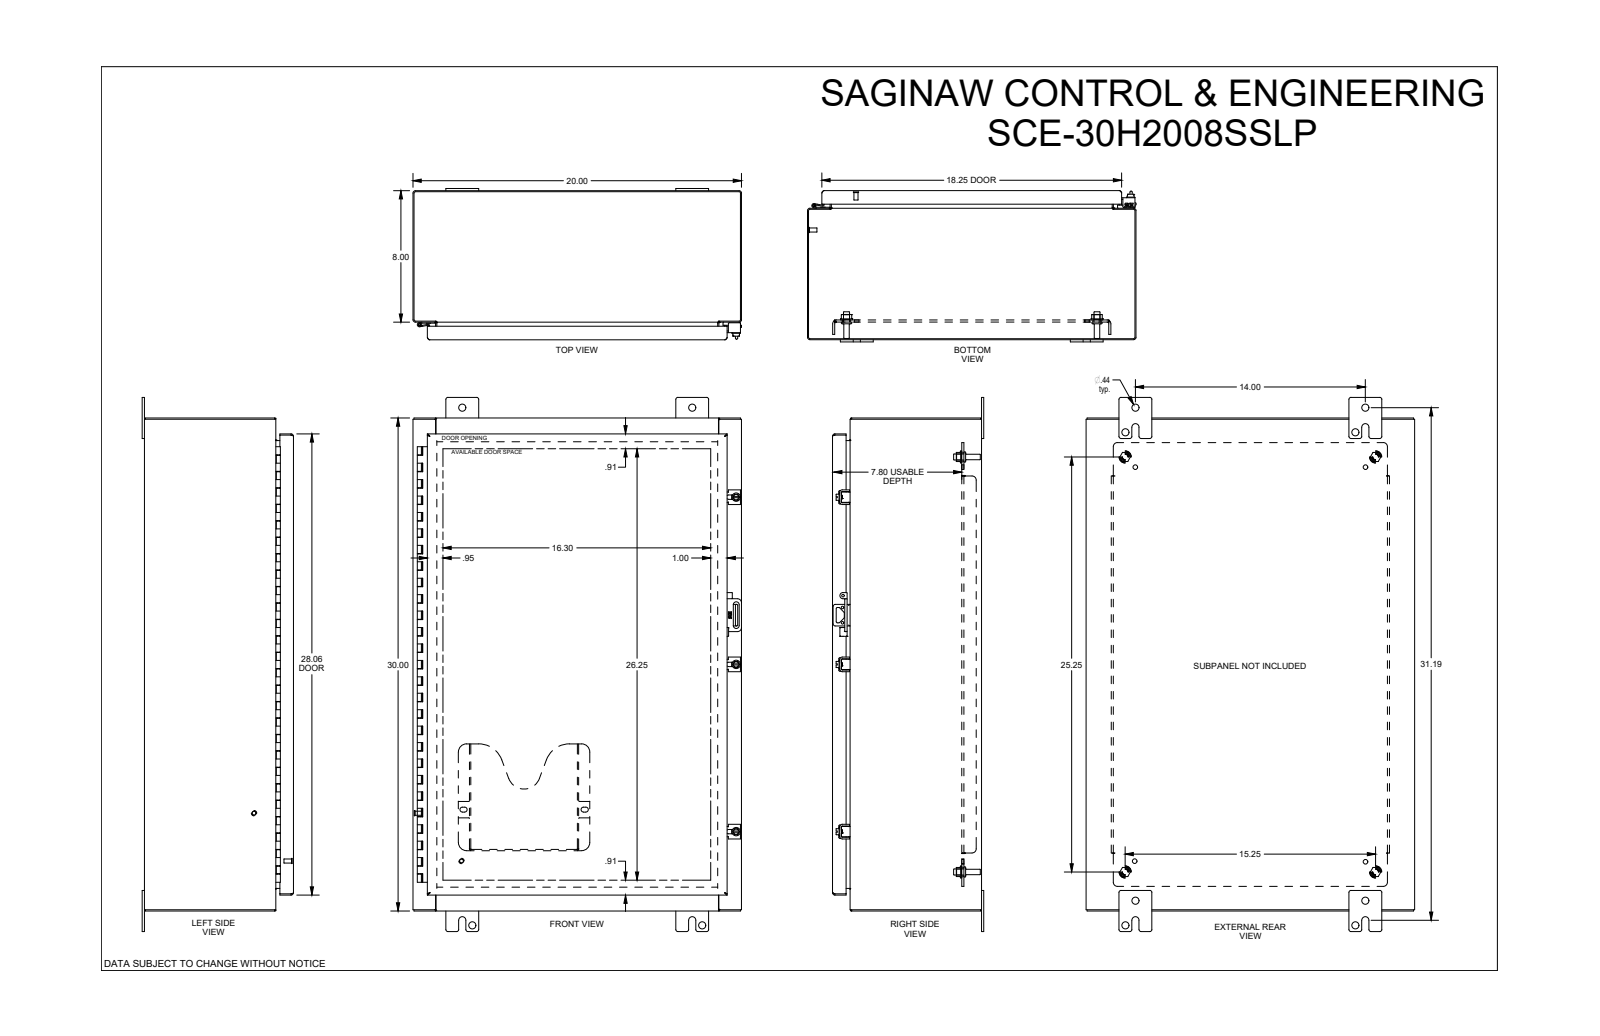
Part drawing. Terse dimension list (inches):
name: SCE-30H2008SSLP
written by: SolidWorks 2019 (CONFIG_CONTROL_DESIGN)
unit: in
bodies: 0 solids, 3793 faces (1553 planar, 790 cylindrical, 1450 other)
size: 32.5 × 20 × 9.208
holes: 8× ⌀0.437, 6× ⌀0.25, 5× ⌀0.19, 5× ⌀0.193, 5× ⌀0.203, 4× ⌀0.281, 4× ⌀0.367, 4× ⌀0.5, 2× ⌀0.16, 1× ⌀0.13, 1× ⌀0.132
bosses: 8× ⌀0.248, 6× ⌀0.563, 5× ⌀0.256, 5× ⌀0.188, 4× ⌀0.366, 4× ⌀0.332, 4× ⌀0.25, 3× ⌀0.507
rounds: 148× R0.01, 44× R0.015, 36× R0.029, 29× R0.06, 27× R0.03, 27× R0.125, 22× R0.04, 14× R0.07
face distances: 0.075, 8.998, 8.923, 0.075, 8.998, 9.073, 19.925, 7.923, 1.2, 1.125
hole spacings: 14, 0.515, 0.875, 6.375, 6.375, 12.75, 17.815, 28.649
